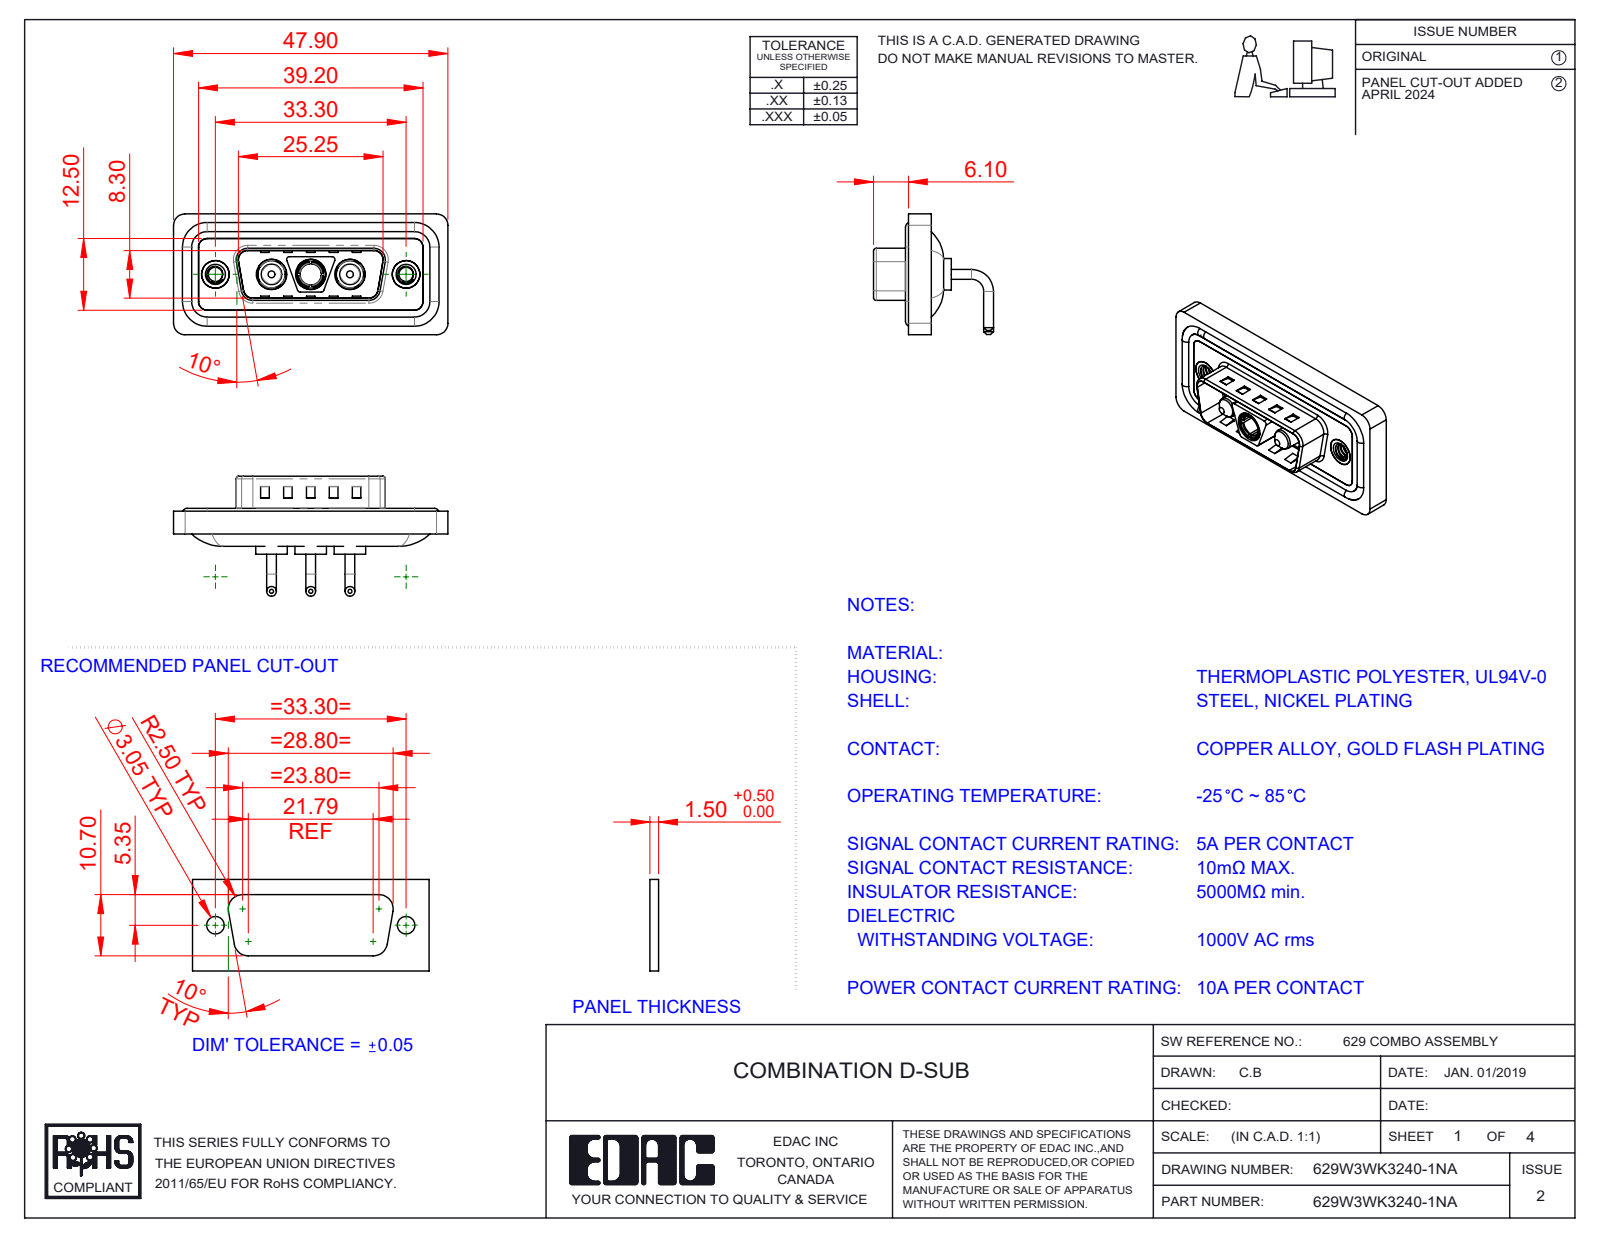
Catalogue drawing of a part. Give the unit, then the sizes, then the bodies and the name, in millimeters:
Units: millimetres
Overall size (bounding box): 47.9 × 21.1 × 20.95
Round holes (diameter × count): ⌀4.85 ×3, ⌀5.3 ×3, ⌀2.5 ×2, ⌀4 ×2, ⌀4.8 ×2, ⌀5 ×2, ⌀3.7 ×1
Round bosses / shafts (diameter × count): ⌀1.7 ×6, ⌀1.6 ×4, ⌀5.5 ×3, ⌀5.2 ×3, ⌀4.75 ×3, ⌀3.75 ×3, ⌀4.9 ×2, ⌀3.6 ×2
Partial cylindrical surfaces — rounded edges, fillets, slot ends (radius × count): R2 ×20, R1.5 ×18, R0.5 ×12, R1.6 ×8, R0.25 ×4, R0.6 ×4, R0.65 ×4, R0.9 ×4
Main face-to-face distances: 0.4, 2.9, 0.8, 1.1, 2.1, 1.6, 4.5, 3.1, 2.5, 1.5
Hole centre spacings: 6.85, 9.8, 16.65, 23.5, 13.7, 33.3
Volume: 5 712 mm³ · Surface area: 9 264 mm²
Bodies: 13 solids, 615 faces (231 planar, 254 cylindrical, 130 other)
Part name (STEP PRODUCT): 629Combo Shell Front_15 Contacts; 629Combo Waterproof Housing_15 Contacts; 629Combo Housing_3WK3; 629Combo Threaded Rivet_A (+4 more)
STEP written by: SolidWorks 2023 (CONFIG_CONTROL_DESIGN)
